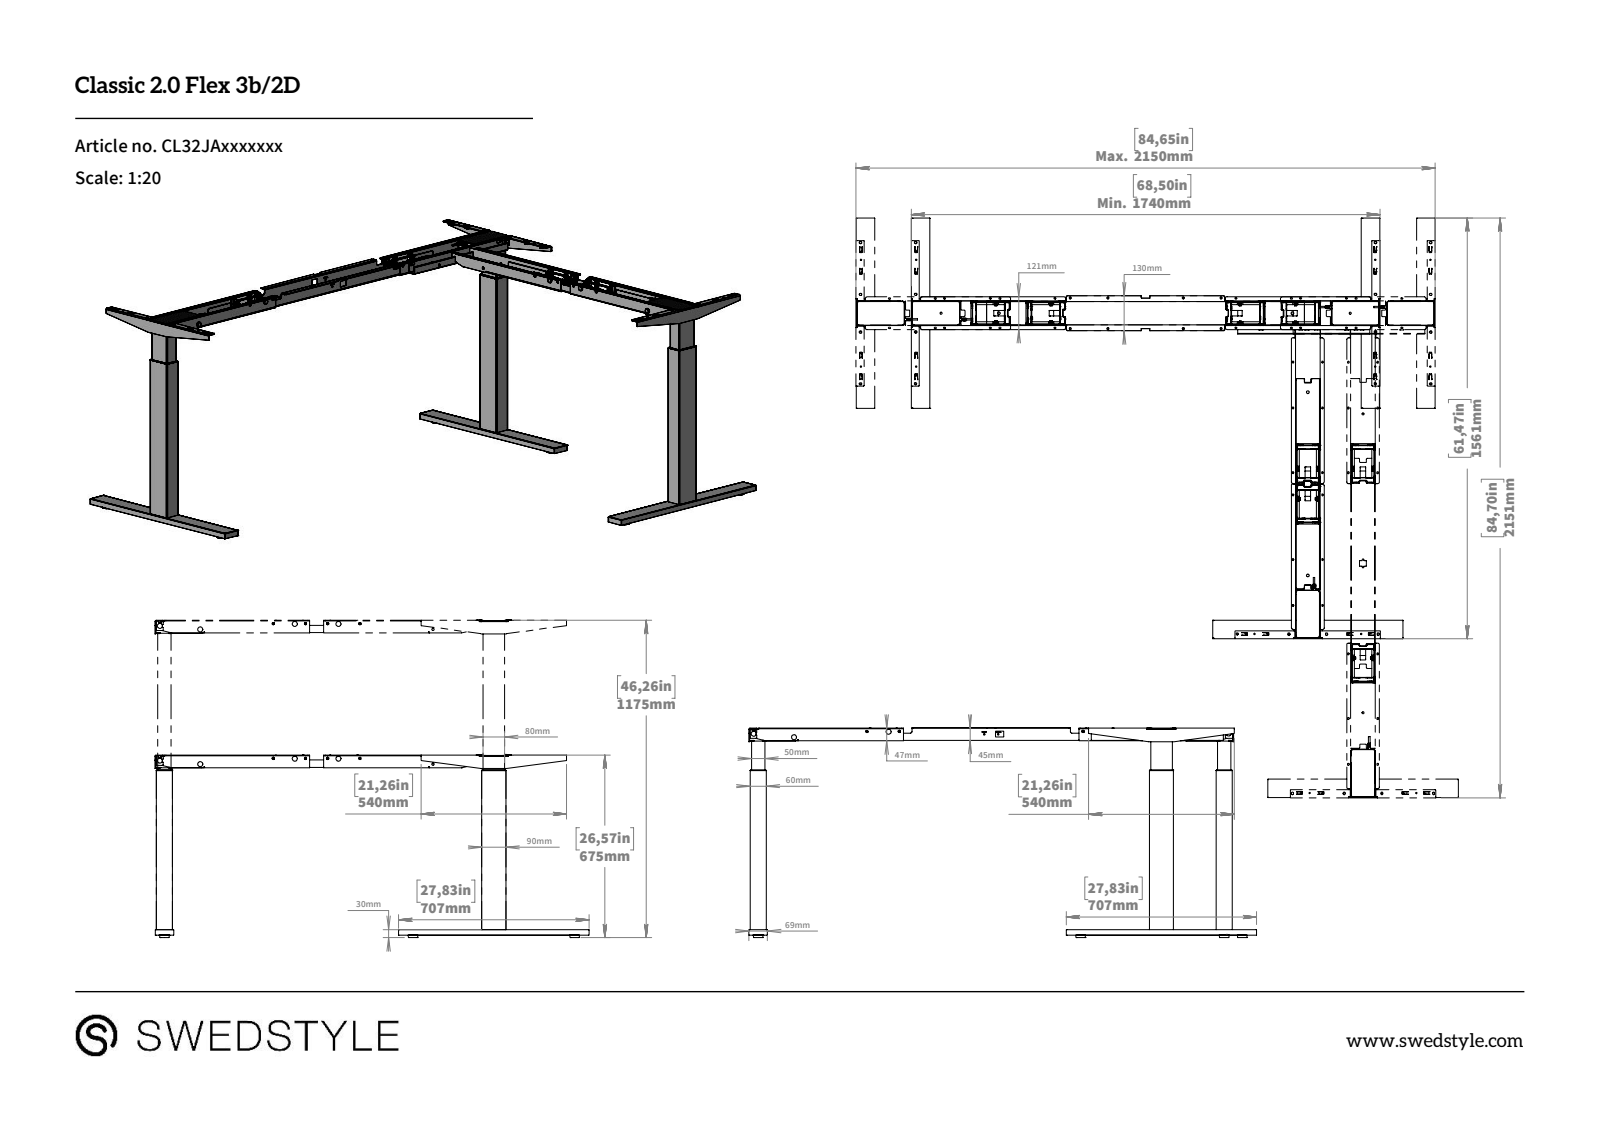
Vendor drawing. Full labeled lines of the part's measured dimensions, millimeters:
Part name (STEP PRODUCT): CL32JAxxxxxxx_Fl174_Fl115
STEP written by: SolidWorks 2015 (CONFIG_CONTROL_DESIGN)
Units: millimetres
Bodies: 0 solids, 2048 faces (1027 planar, 715 cylindrical, 306 other)
Overall size (bounding box): 1885.5 × 1611.38 × 727.9
Round holes (diameter × count): ⌀16 ×12, ⌀6 ×11, ⌀8 ×10, ⌀14 ×6, ⌀7 ×5, ⌀5 ×4, ⌀10 ×4, ⌀8.5 ×1
Round bosses / shafts (diameter × count): ⌀8.5 ×3, ⌀5.5 ×3
Partial cylindrical surfaces — rounded edges, fillets, slot ends (radius × count): R0.5 ×150, R3 ×41, R1 ×40, R2 ×38, R4 ×37, R2.75 ×31, R3.5 ×22, R7 ×20
Main face-to-face distances: 2, 2.5, 4, 90.5, 655.3, 0.5, 1, 92.5, 93, 5
Hole centre spacings: 140, 180.54, 280, 302.32, 114, 106.53, 236.96, 271.06
